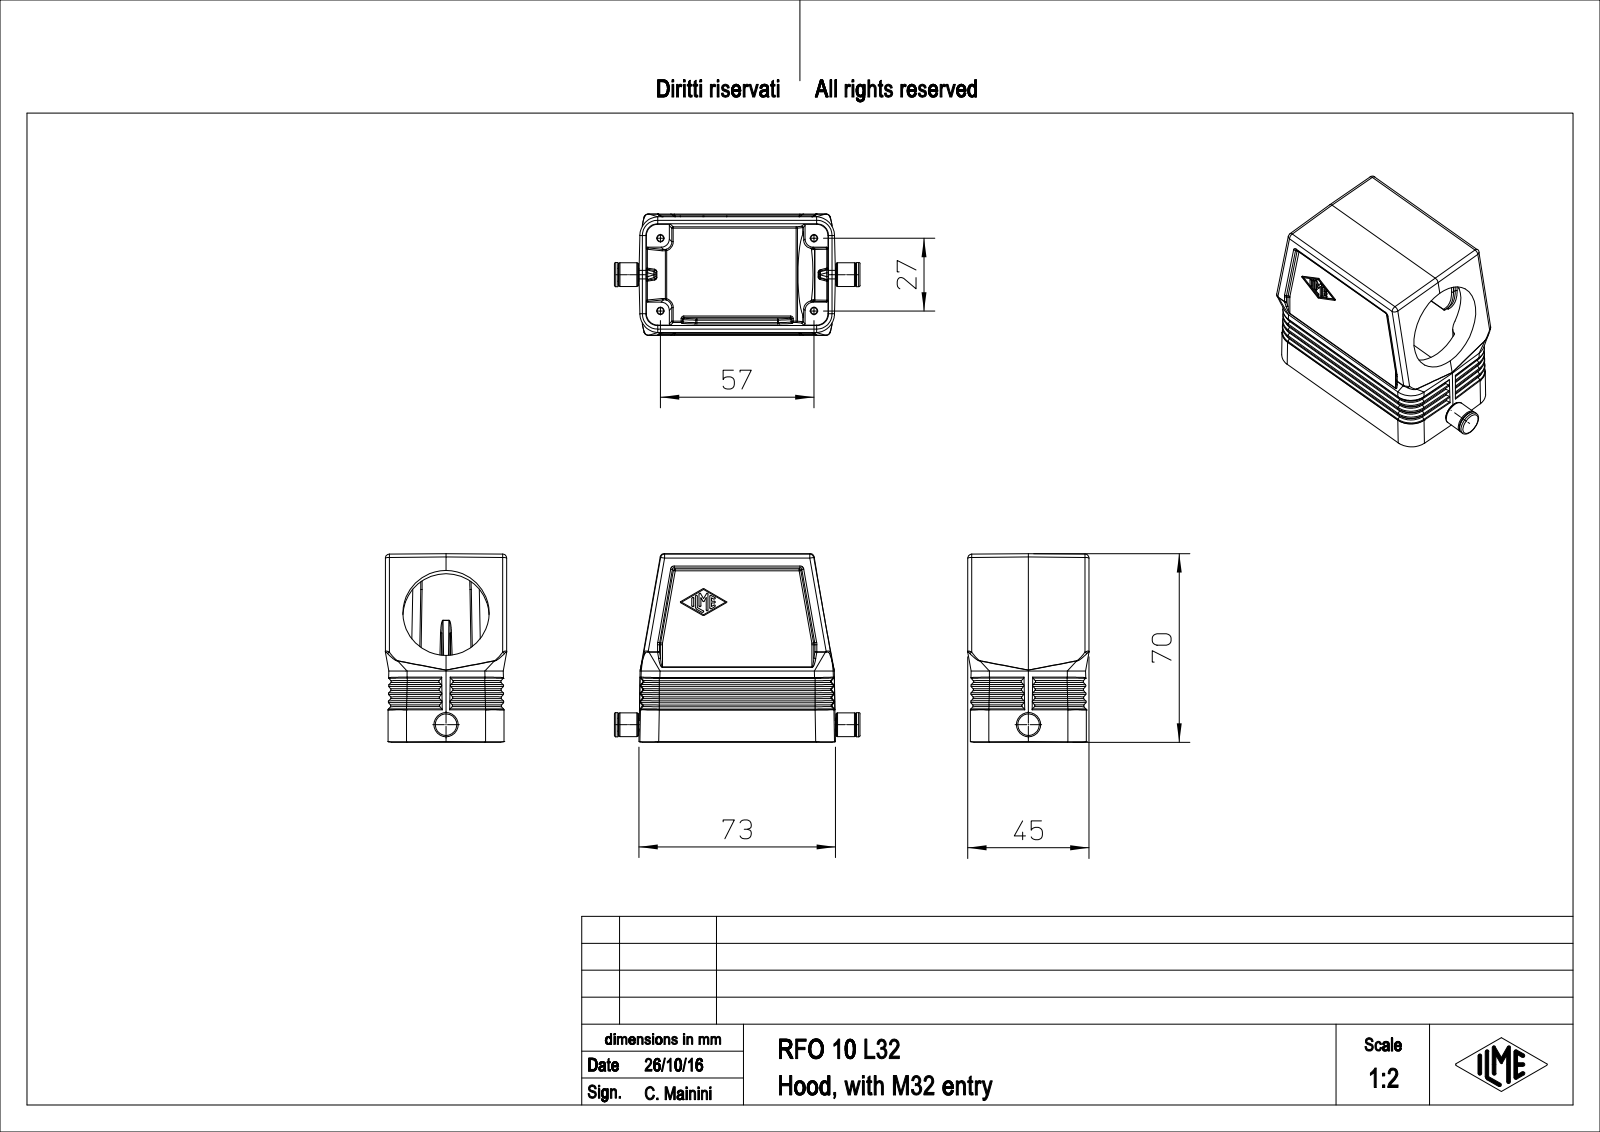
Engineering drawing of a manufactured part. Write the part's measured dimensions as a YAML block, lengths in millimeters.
part_name: "RFO_10_L32"
step_written_by: "PTC Creo Elements/Direct Modeling 19.0E 27-Jun-2016 (C) Parametric Technology GmbH (AUTOMOTIVE_DESIGN)"
units: millimeters
bodies: {solids: 1, faces: 431, planar: 149, cylindrical: 100, other: 182}
overall_size: [91.19, 70, 45]
volume: 65613
surface_area: 33429
round_holes:
  - {diameter: 2.75, count: 4}
  - {diameter: 32, count: 1}
round_bosses_or_shafts:
  - {diameter: 9, count: 1}
  - {diameter: 8.8, count: 1}
  - {diameter: 4.8, count: 1}
  - {diameter: 3.2, count: 1}
partial_cylinders:
  - {radius: 0.5, count: 16}
  - {radius: 1, count: 14}
  - {radius: 1.5, count: 10}
  - {radius: 7, count: 8}
  - {radius: 3, count: 4}
  - {radius: 4.2, count: 4}
  - {radius: 6, count: 4}
  - {radius: 20, count: 1}
face_to_face_distances: [43, 8.5, 1.91, 2, 44, 1, 4, 45, 6, 11.35]
hole_center_spacings: [27, 57, 63.07]
